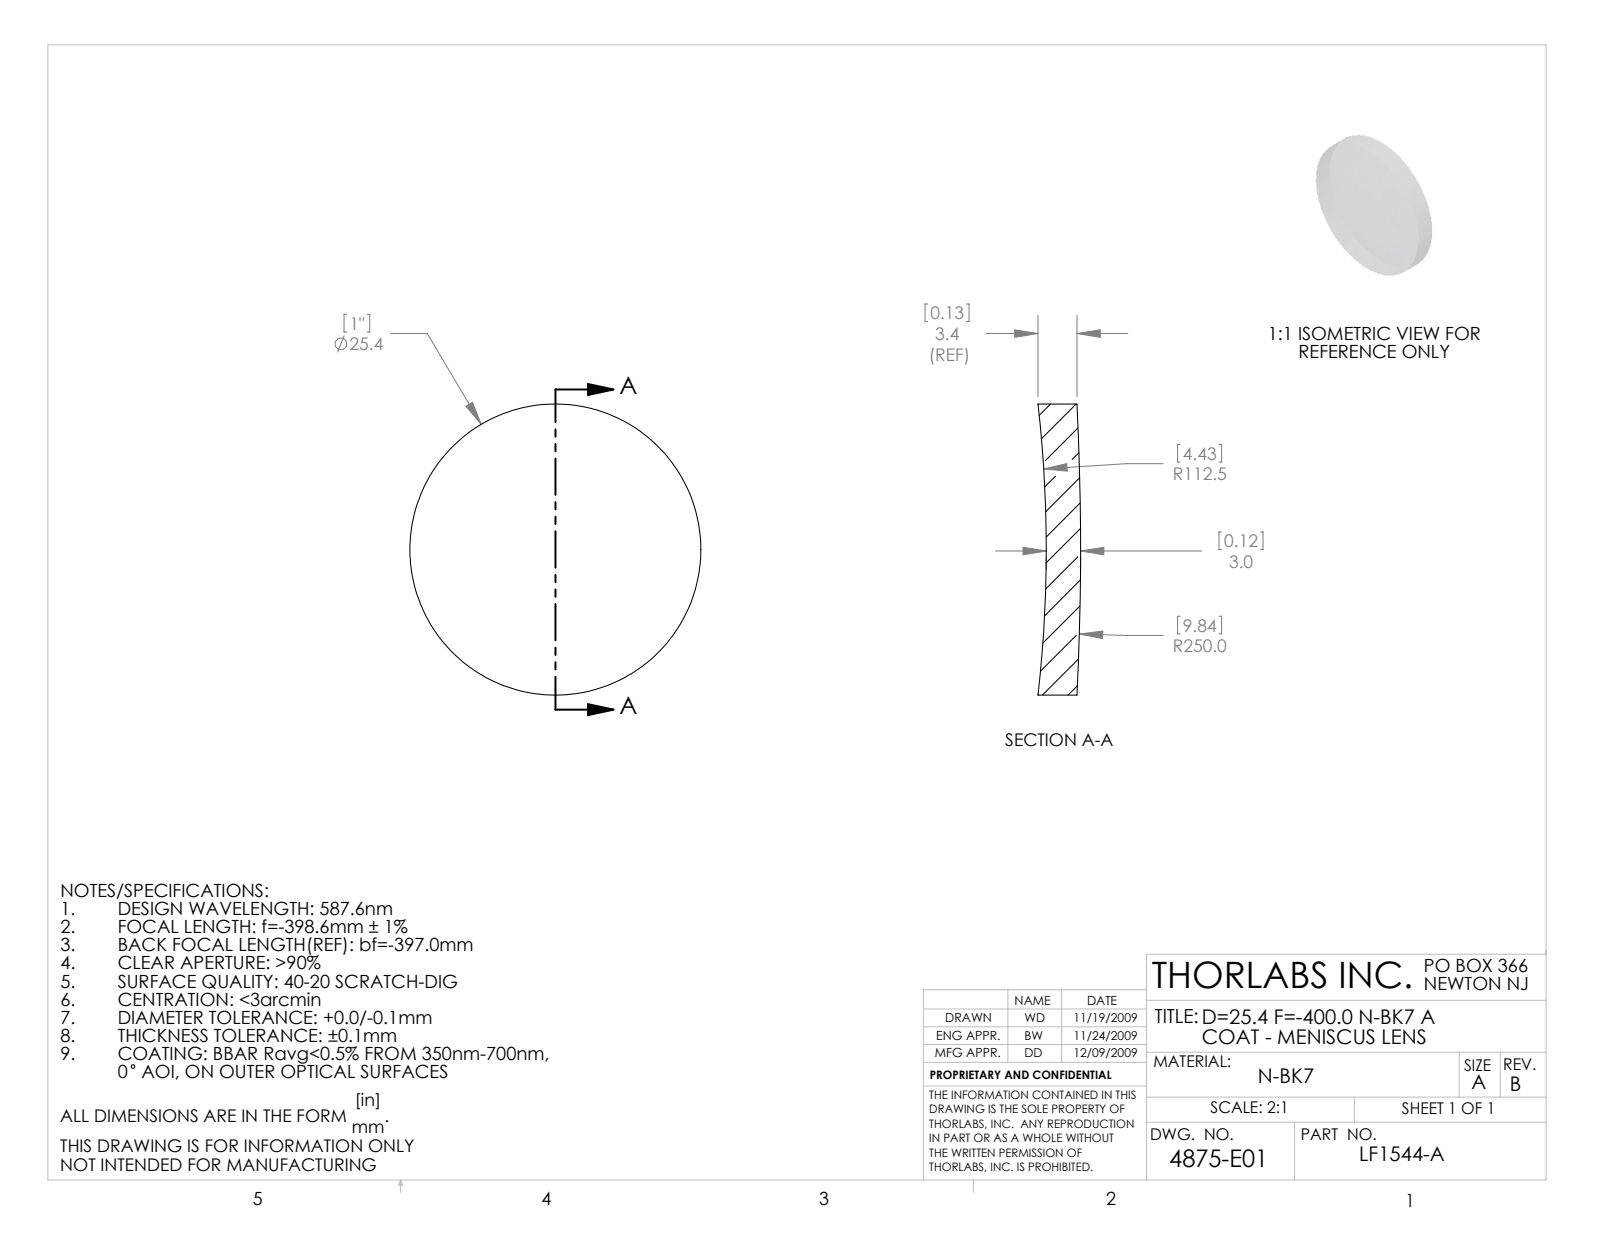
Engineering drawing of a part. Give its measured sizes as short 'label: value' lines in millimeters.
name: 4875-E0W
written by: SolidWorks 2009 (AUTOMOTIVE_DESIGN)
unit: mm
bodies: 1 solid, 6 faces (0 planar, 2 cylindrical, 4 other)
size: 25.4 × 25.4 × 3.72
volume: 1 620 mm³; area: 1 286 mm²
bosses: 1× ⌀25.4
